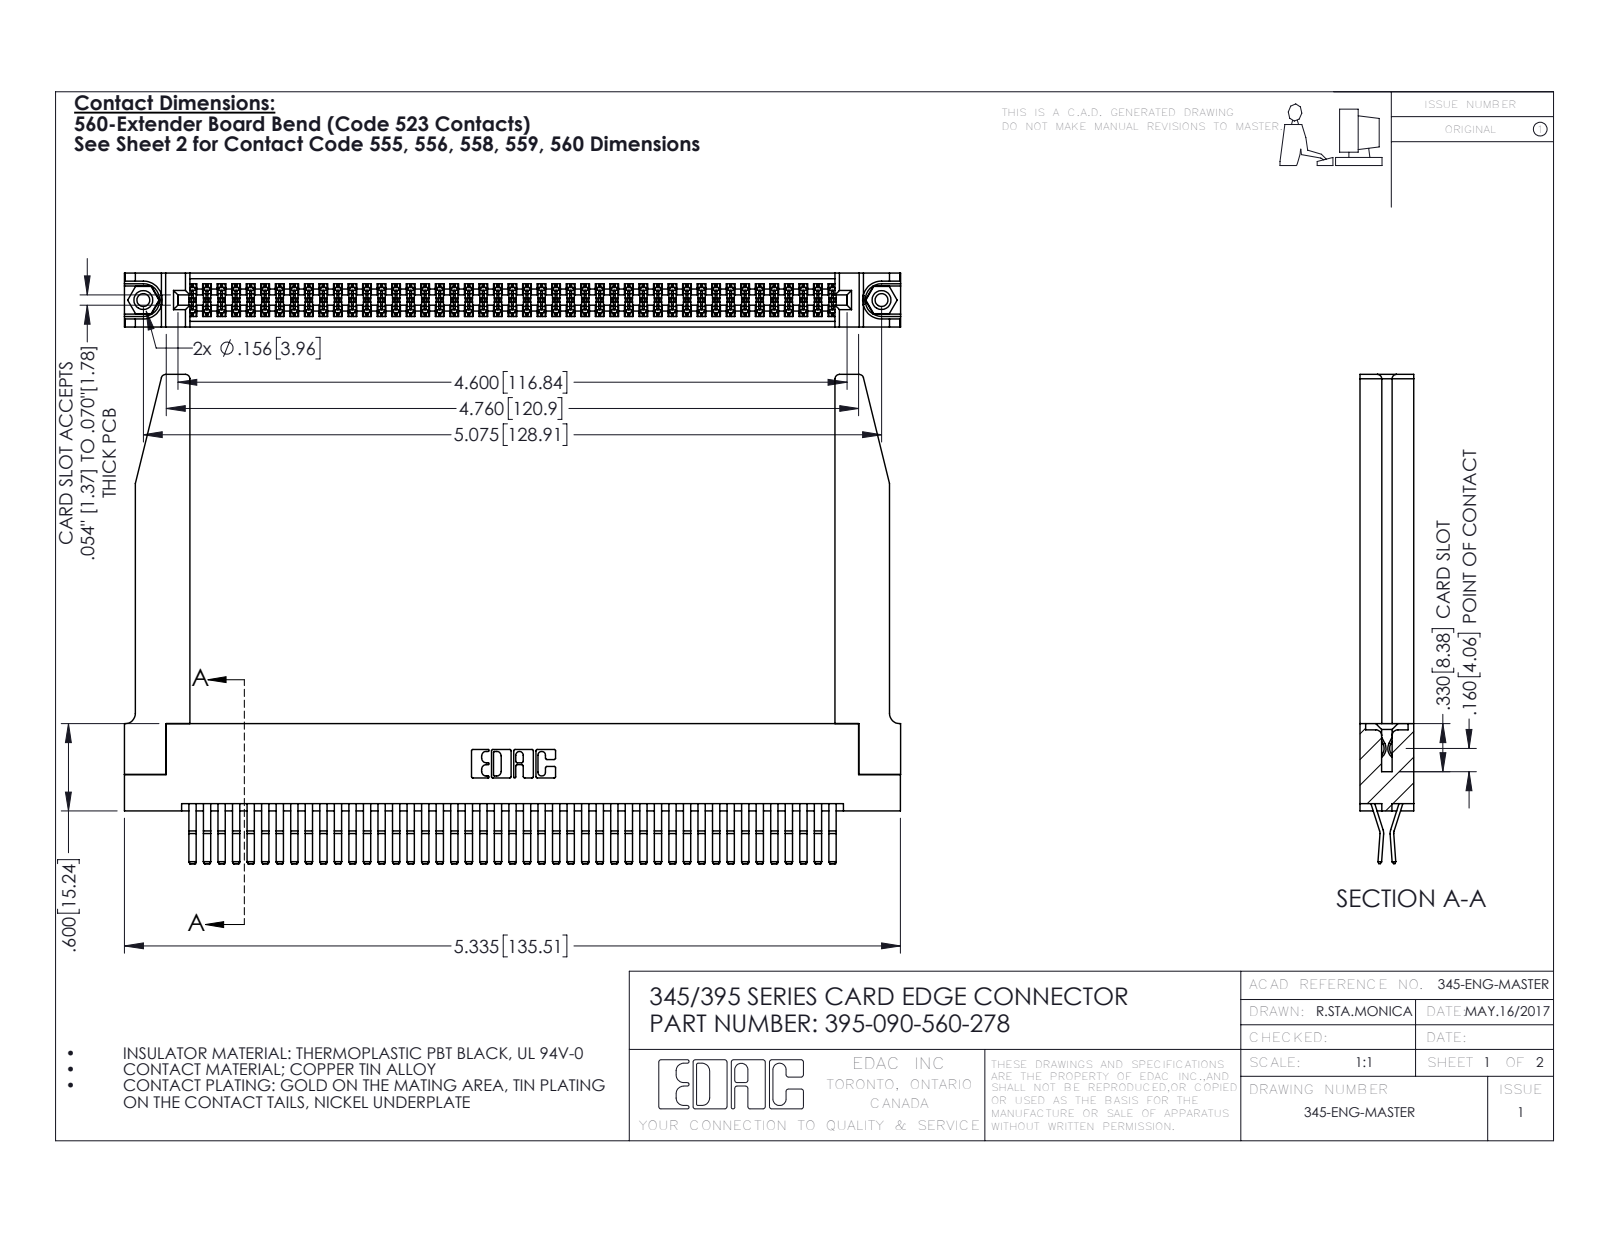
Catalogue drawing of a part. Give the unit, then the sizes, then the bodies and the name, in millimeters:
Units: millimetres
Overall size (bounding box): 135.5 × 85.4 × 9.4
Round holes (diameter × count): ⌀2.3 ×2, ⌀3.2 ×2, ⌀4 ×2, ⌀1.6 ×1
Round bosses / shafts (diameter × count): ⌀3.9 ×2
Partial cylindrical surfaces — rounded edges, fillets, slot ends (radius × count): R0.2 ×135, R0.3 ×22, R0.8 ×8, R0.2 ×6, R0.8 ×6, R0.7 ×3, R0.3 ×2, R0.4 ×2
Main face-to-face distances: 9.4, 1.8, 7.6, 0.6, 5.1, 2.5, 6.9, 5.7, 3.8, 3.8
Hole centre spacings: 6.9, 122.9, 128.9
Volume: 21 550 mm³ · Surface area: 28 790 mm²
Bodies: 95 solids, 5040 faces (3192 planar, 1796 cylindrical, 52 other)
Part name (STEP PRODUCT): 345-220-078_345-220-078; 345 Part_Flush Mounting Lugs - 0.156 Dia-TH; 345-292-001_560 Tail; 395-090-560-278 (+1 more)
STEP written by: SolidWorks 2016 (CONFIG_CONTROL_DESIGN)
